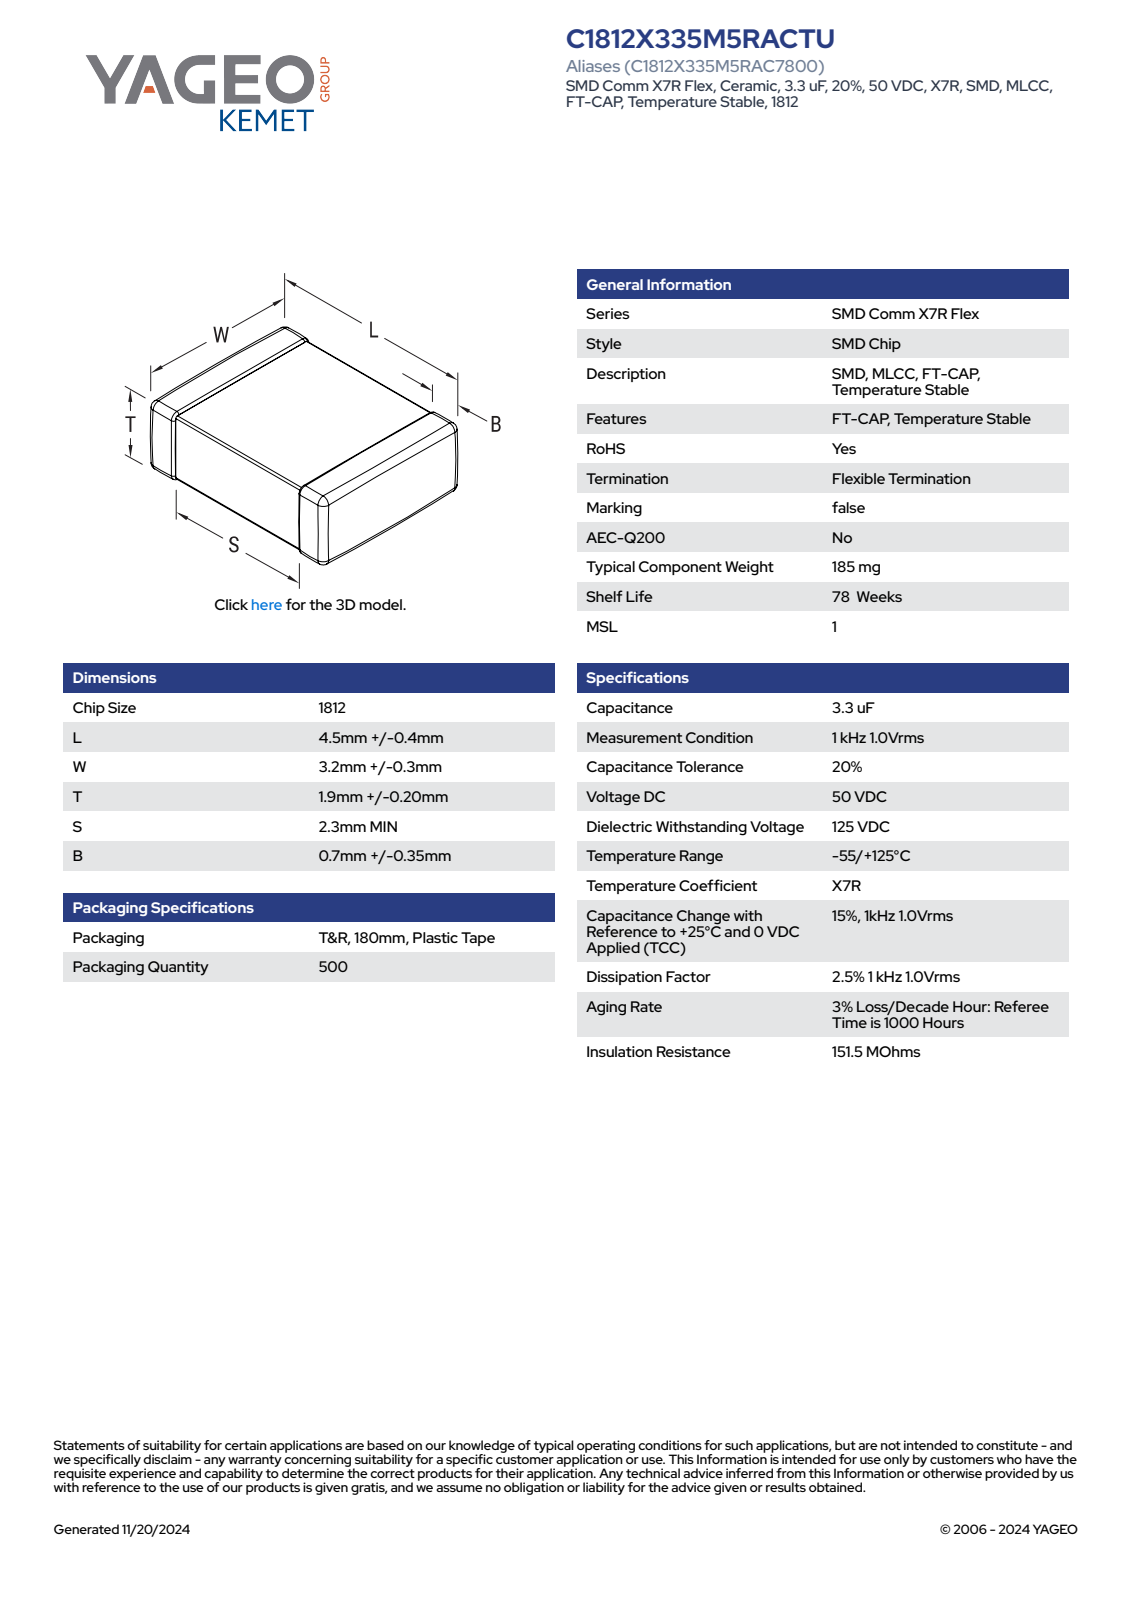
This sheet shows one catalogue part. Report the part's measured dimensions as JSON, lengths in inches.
{"part_name": "CCS_CCSTD_1812_L4.9W3.5T2.1B0.7", "step_written_by": "SolidWorks 2021 (AUTOMOTIVE_DESIGN)", "units": "inches", "bodies": {"solids": 4, "faces": 121, "planar": 71, "cylindrical": 34, "other": 16}, "overall_size": [0.193, 0.138, 0.083], "volume_in3": 0.002, "surface_area_in2": 0.11, "face_to_face_distances": [0.08, 0.077, 0.135, 0.193, 0.083, 0.132, 0.138, 0.02, 0.089, 0.084]}
